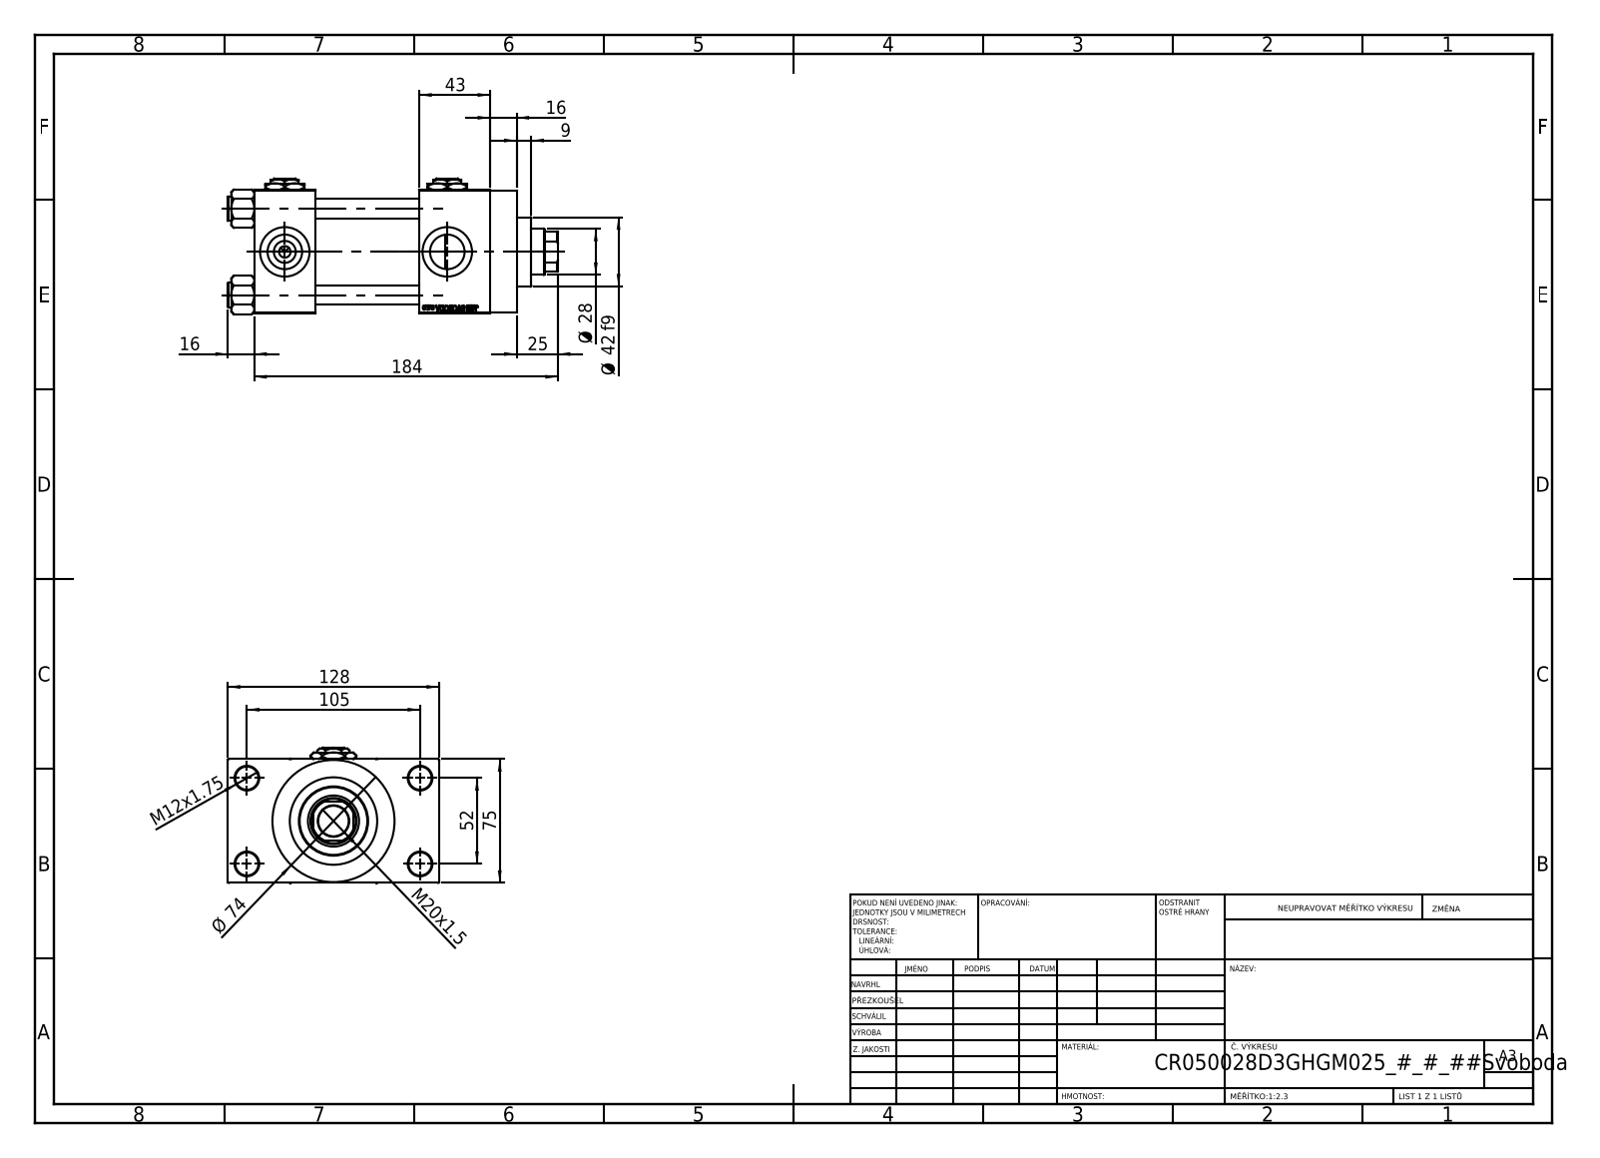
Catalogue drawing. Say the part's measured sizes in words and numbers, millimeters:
The part is named "NUT_M5_D; V215CR_VCP_D; V215_VC_A; Zatka_pro_OIL_PORT (+2 more)". Its 3-D file was written by "SolidWorks 2019 (CONFIG_CONTROL_DESIGN)". It is 13 solids with 1204 faces: 545 planar, 99 cylindrical and 560 other. Overall it measures 200 by 128 by 82.27 millimeters. Its volume is 809 661 cubic millimeters and its surface area 177 701 square millimeters. Round holes: 4 of diameter 12, 4 of diameter 14, 4 of diameter 20.96, 4 of diameter 30, 3 of diameter 7, 1 of diameter 18.5, 1 of diameter 28, 1 of diameter 31, 1 of diameter 41, 1 of diameter 50, 1 of diameter 53. Round bosses or shafts: 4 of diameter 15, 1 of diameter 74, 1 of diameter 56, 1 of diameter 42. Partial cylindrical surfaces (rounded edges, fillets, slot ends): 1 of radius 13.5. The main face-to-face distances are 75, 63, 37, 100, 26.5, 143, 106, 43, 101.5, 16. The hole center spacings are 26.35, 36.98, 52.3, 58.43, 58.59, 78.65, 94.37, 52.
